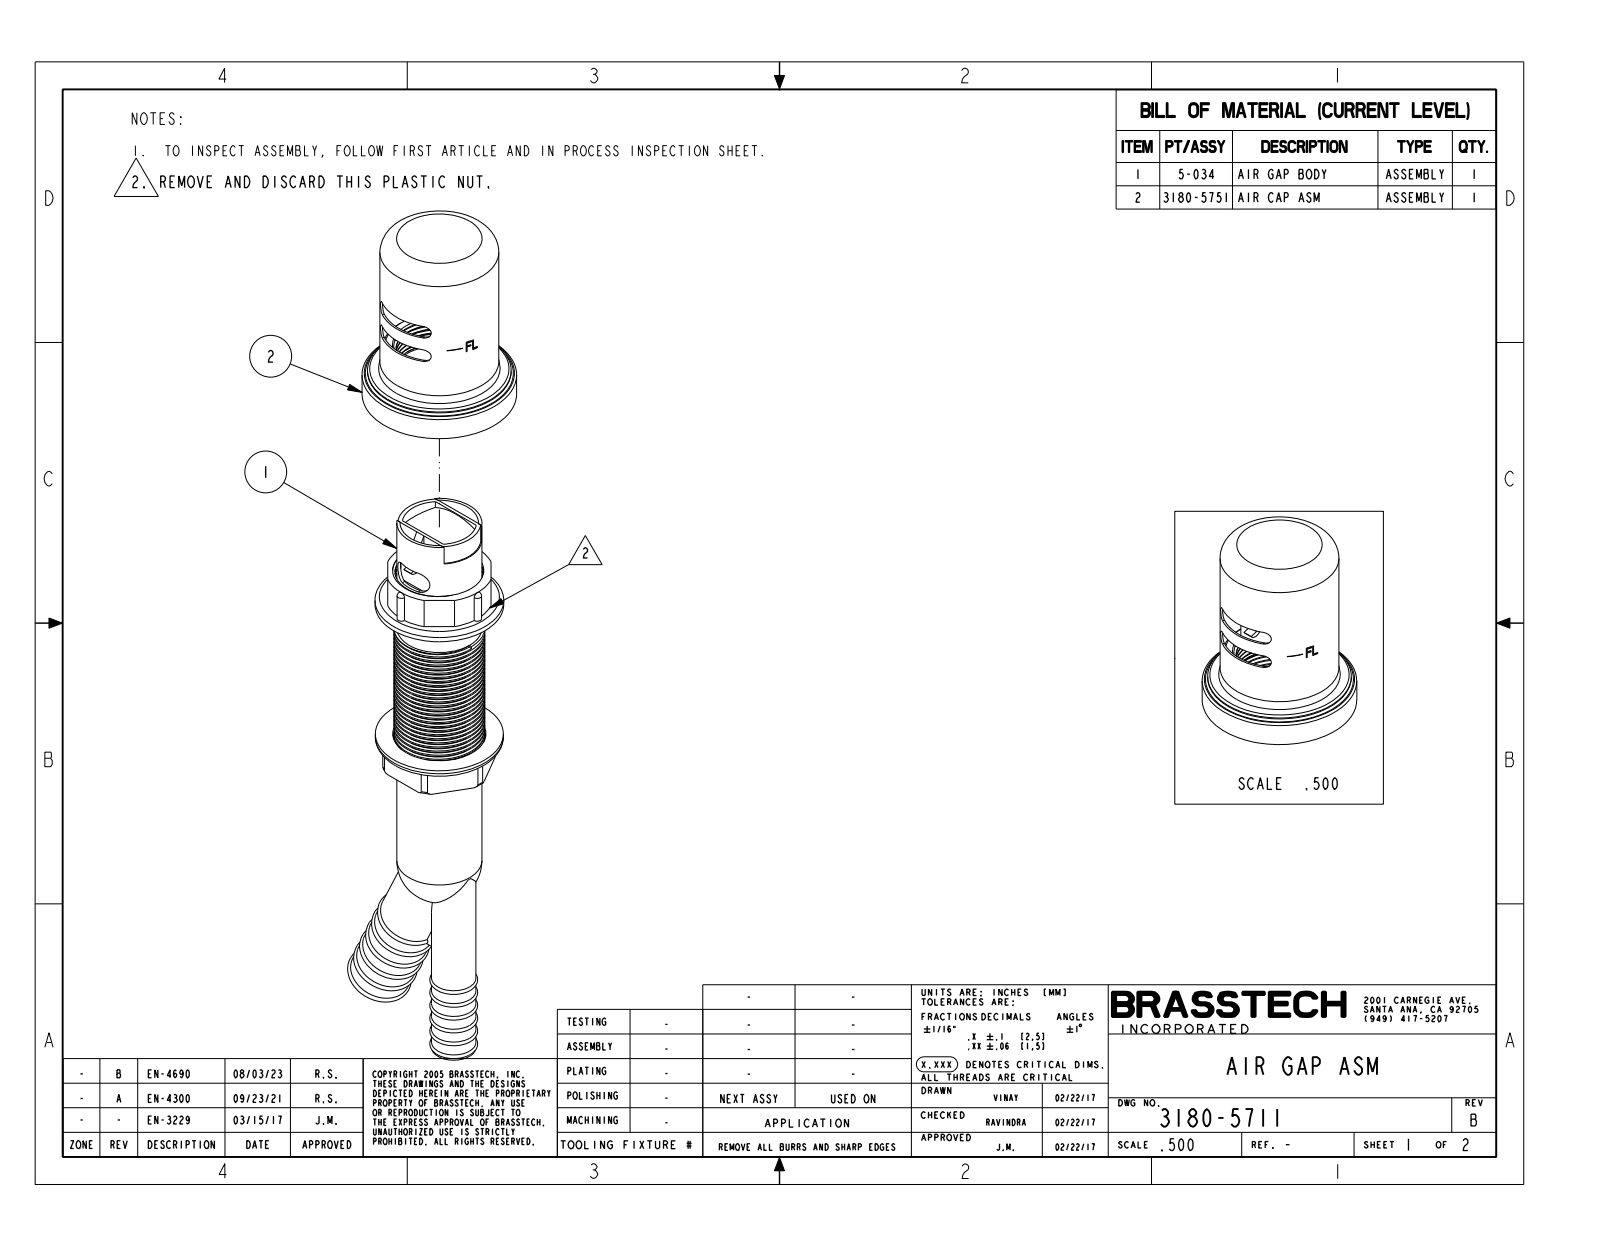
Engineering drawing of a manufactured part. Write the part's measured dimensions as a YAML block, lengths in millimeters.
part_name: "3180-5711"
step_written_by: "CREO PARAMETRIC BY PTC INC, 2018400 (AUTOMOTIVE_DESIGN)"
units: millimeters
bodies: {solids: 2, faces: 276, planar: 67, cylindrical: 130, other: 79}
overall_size: [223.6, 67.2, 54]
volume: 169600
surface_area: 52040
round_holes:
  - {diameter: 30.5, count: 1}
  - {diameter: 32.3, count: 1}
  - {diameter: 32.5, count: 1}
  - {diameter: 40, count: 1}
round_bosses_or_shafts:
  - {diameter: 54, count: 1}
  - {diameter: 50.2, count: 1}
  - {diameter: 45.7, count: 1}
  - {diameter: 44.7, count: 1}
  - {diameter: 41.5, count: 1}
  - {diameter: 32, count: 1}
  - {diameter: 29.7, count: 1}
  - {diameter: 21.7, count: 1}
partial_cylinders:
  - {radius: 1, count: 6}
  - {radius: 2.5, count: 4}
  - {radius: 4, count: 2}
  - {radius: 20.5, count: 1}
face_to_face_distances: [10.8, 23.4, 34.2, 89, 89.8, 65.7, 66.4, 54.9, 55.6, 0.8]
